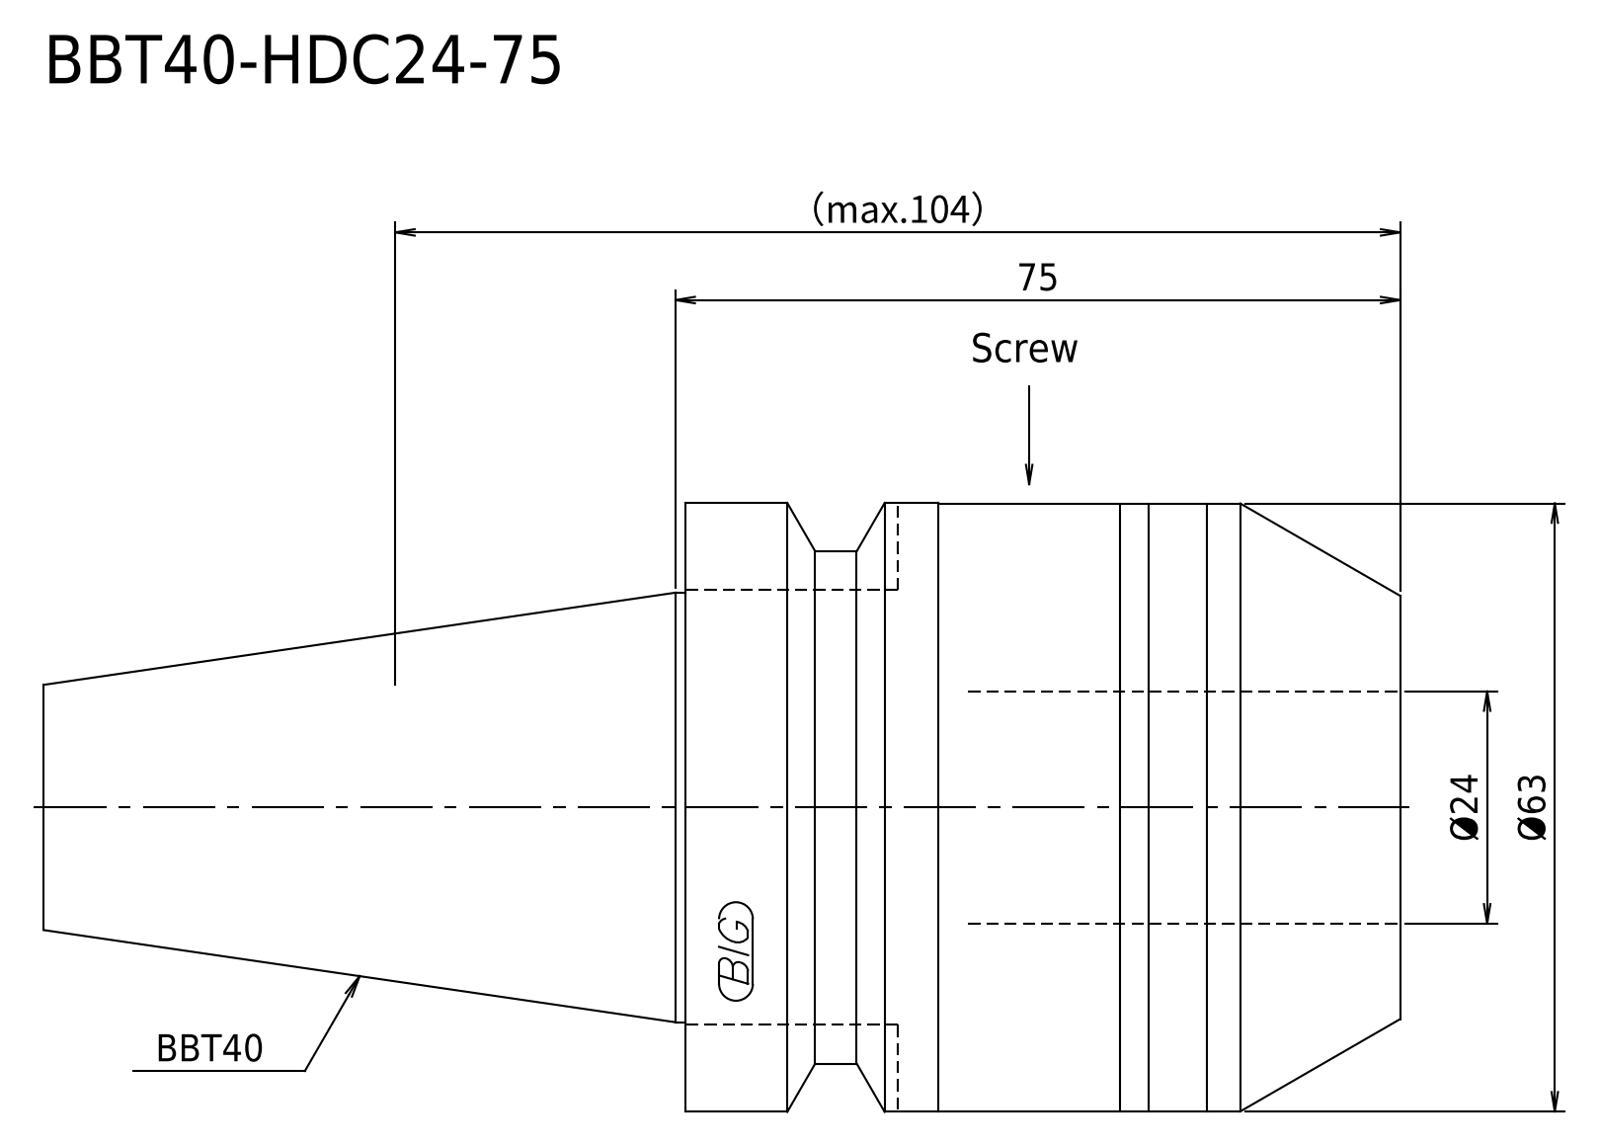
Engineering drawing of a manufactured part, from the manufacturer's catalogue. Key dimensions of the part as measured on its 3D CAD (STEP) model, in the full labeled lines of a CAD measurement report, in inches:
STEP written by: Kubotek KeyCreator V8.5.1 (14335) (CONFIG_CONTROL_DESIGN)
Units: inches
Bodies: 1 solid, 15 faces (4 planar, 5 cylindrical, 6 other)
Overall size (bounding box): 5.528 × 2.48 × 2.48
Volume: 16.62 in³ · Surface area: 40.71 in²
Round bosses / shafts (diameter × count): ⌀2.48 ×1, ⌀2.445 ×1, ⌀2.087 ×1, ⌀1.75 ×1
Main face-to-face distances: 2.886, 0.028, 2.913, 5.528, 5.5, 2.614
